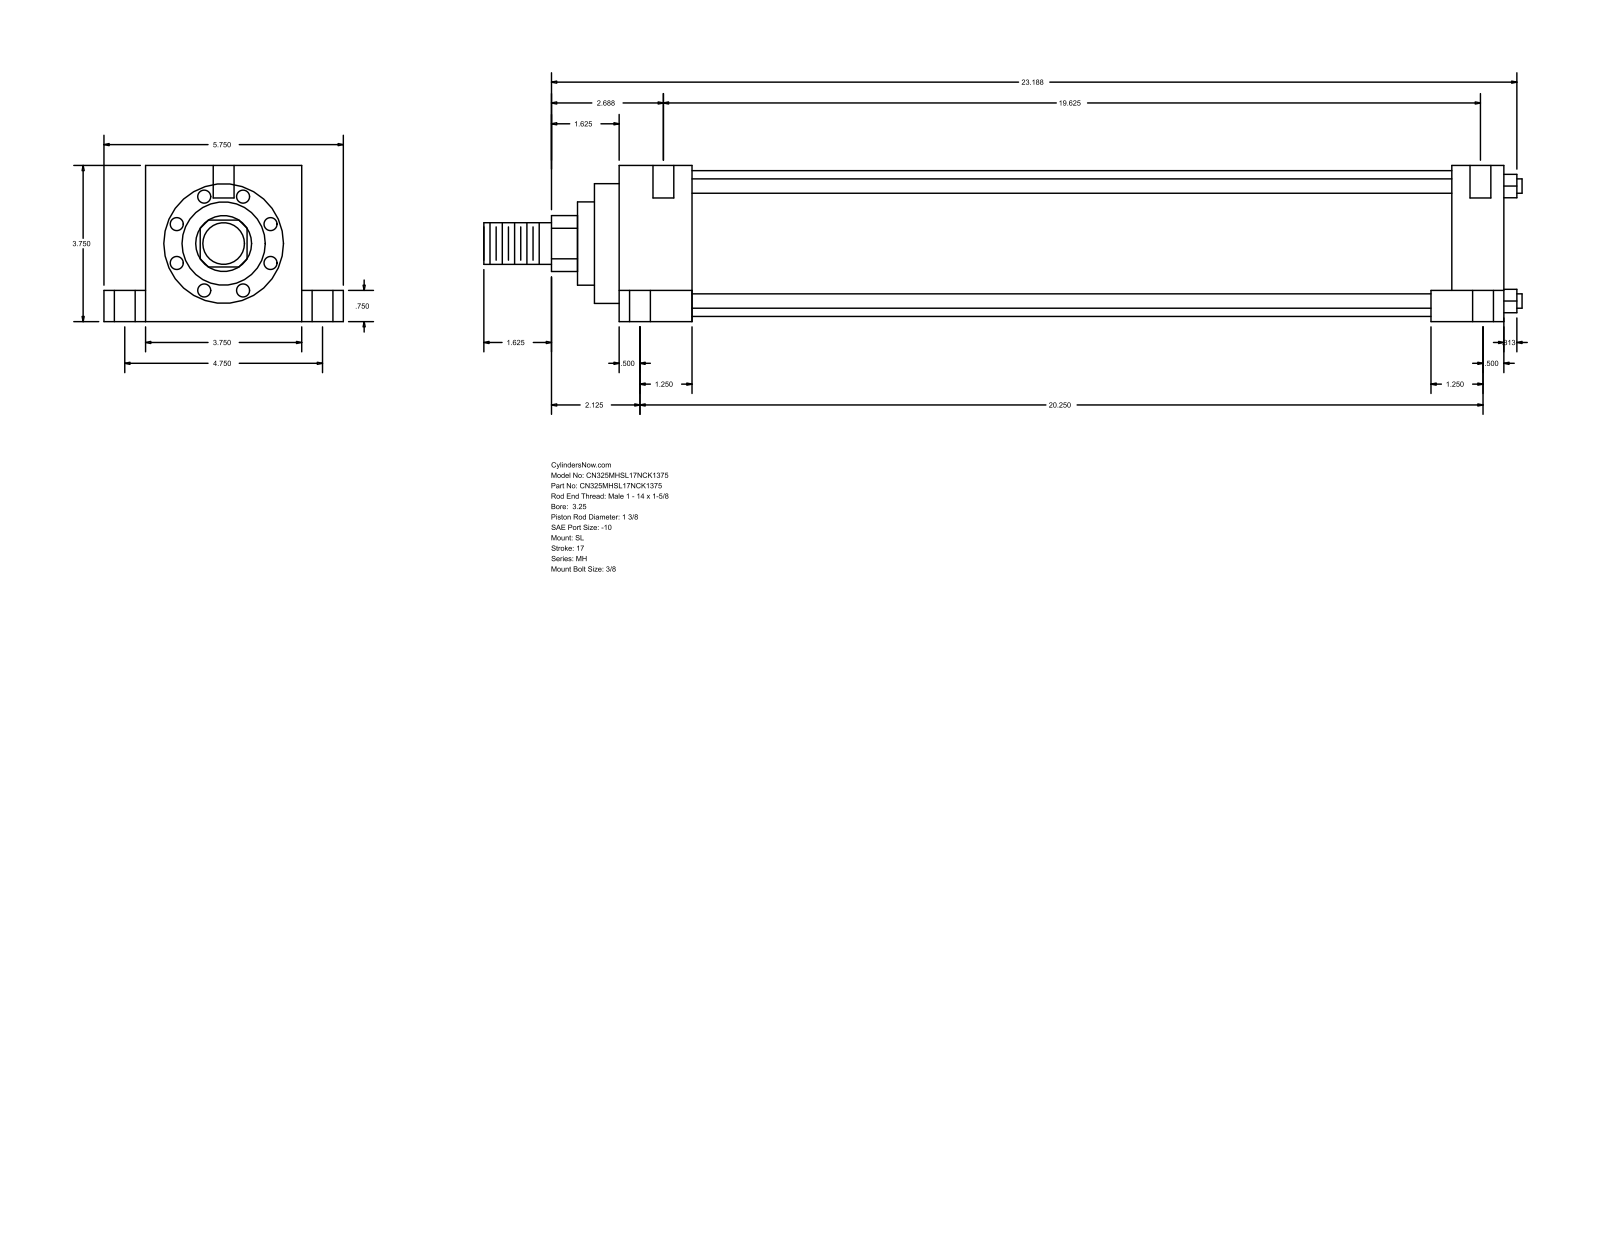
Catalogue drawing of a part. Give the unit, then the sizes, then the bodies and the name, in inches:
Units: inches
Overall size (bounding box): 24.937 × 5.75 × 3.75
Round holes (diameter × count): ⌀0.5 ×6, ⌀0.219 ×4, ⌀0.75 ×4
Round bosses / shafts (diameter × count): ⌀0.345 ×4, ⌀3.5 ×1, ⌀2.875 ×1, ⌀2 ×1, ⌀1.375 ×1, ⌀1 ×1
Partial cylindrical surfaces — rounded edges, fillets, slot ends (radius × count): R0.672 ×1
Main face-to-face distances: 3.75, 21.25, 1.75, 19.5, 1, 4.75, 0.75, 3, 20, 18.25
Hole centre spacings: 2.376, 2.378, 2.427, 2.441, 4.75, 19.831, 19.875, 19.893
Bodies: 0 solids, 110 faces (77 planar, 33 cylindrical, 0 other)
Part name (STEP PRODUCT): MH_SL__0325_1.375
STEP written by: GSSL Pune (CONFIG_CONTROL_DESIGN)
